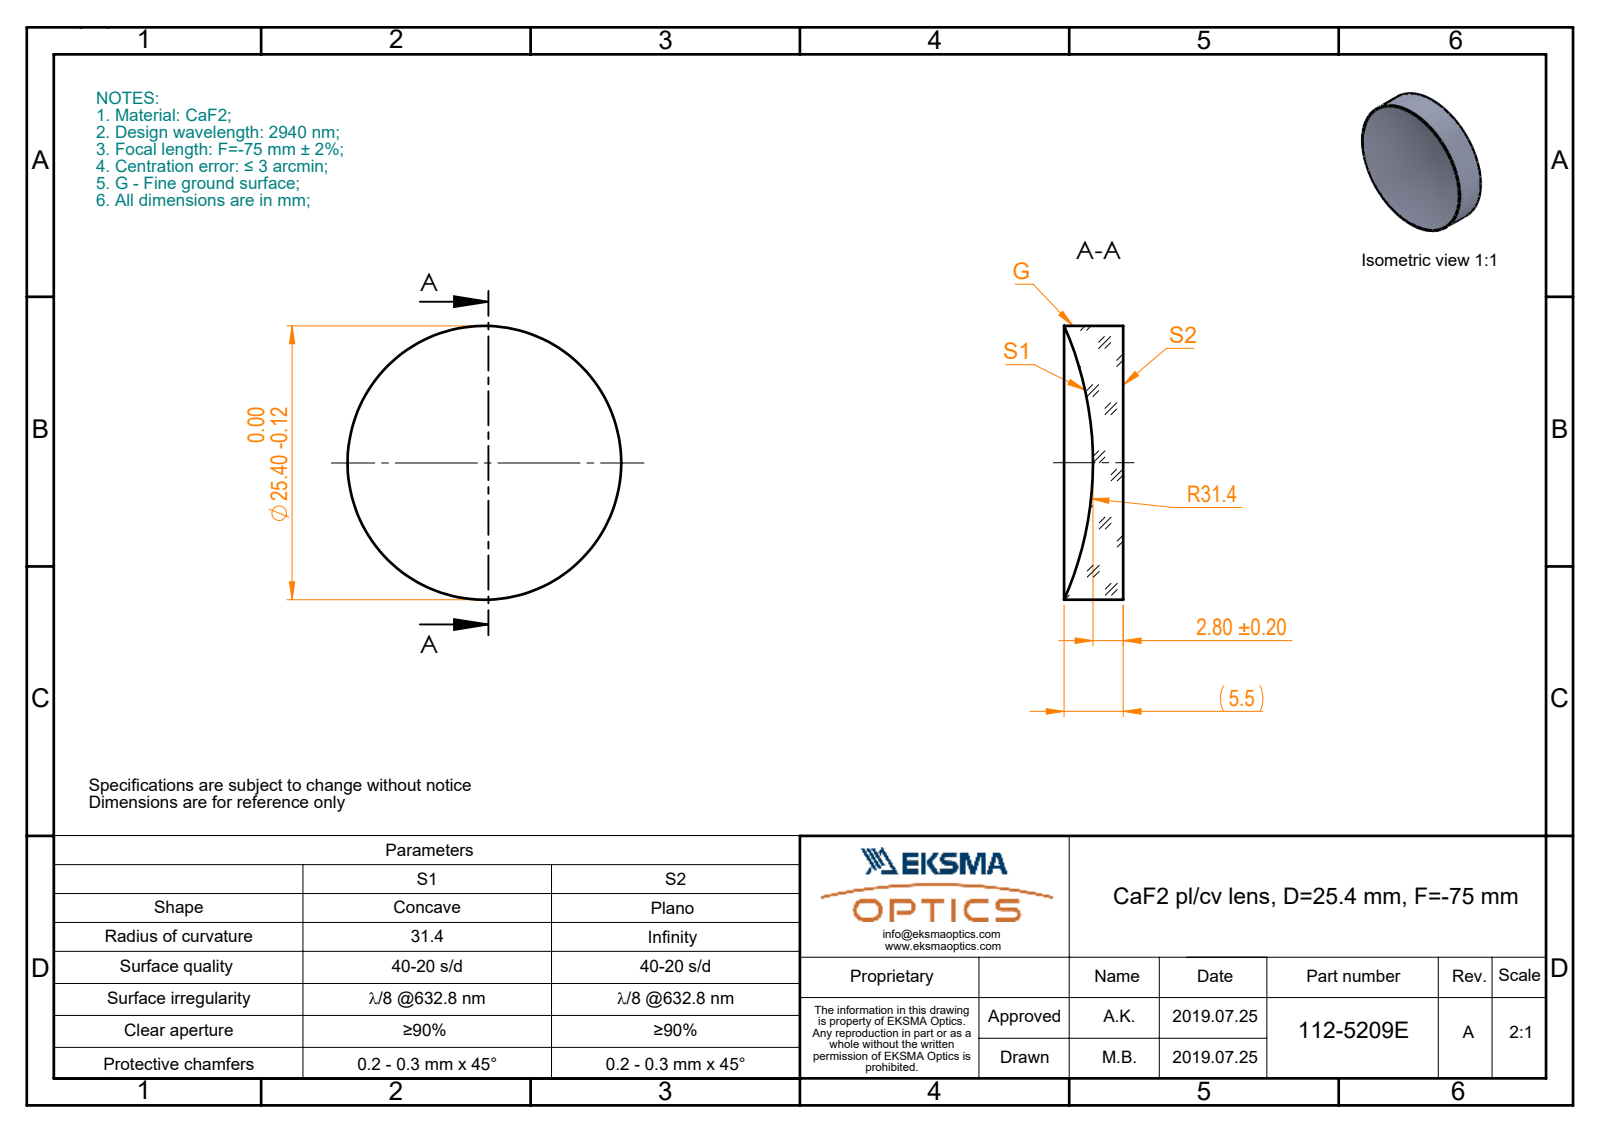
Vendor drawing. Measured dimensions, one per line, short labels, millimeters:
name: 112-5209E CaF2 pl-cv 12.7 F-75
written by: SolidWorks 2017 (CONFIG_CONTROL_DESIGN)
unit: mm
bodies: 1 solid, 5 faces (1 planar, 2 cylindrical, 2 other)
size: 25.4 × 25.4 × 5.49
volume: 2 089 mm³; area: 1 474 mm²
bosses: 1× ⌀25.4
